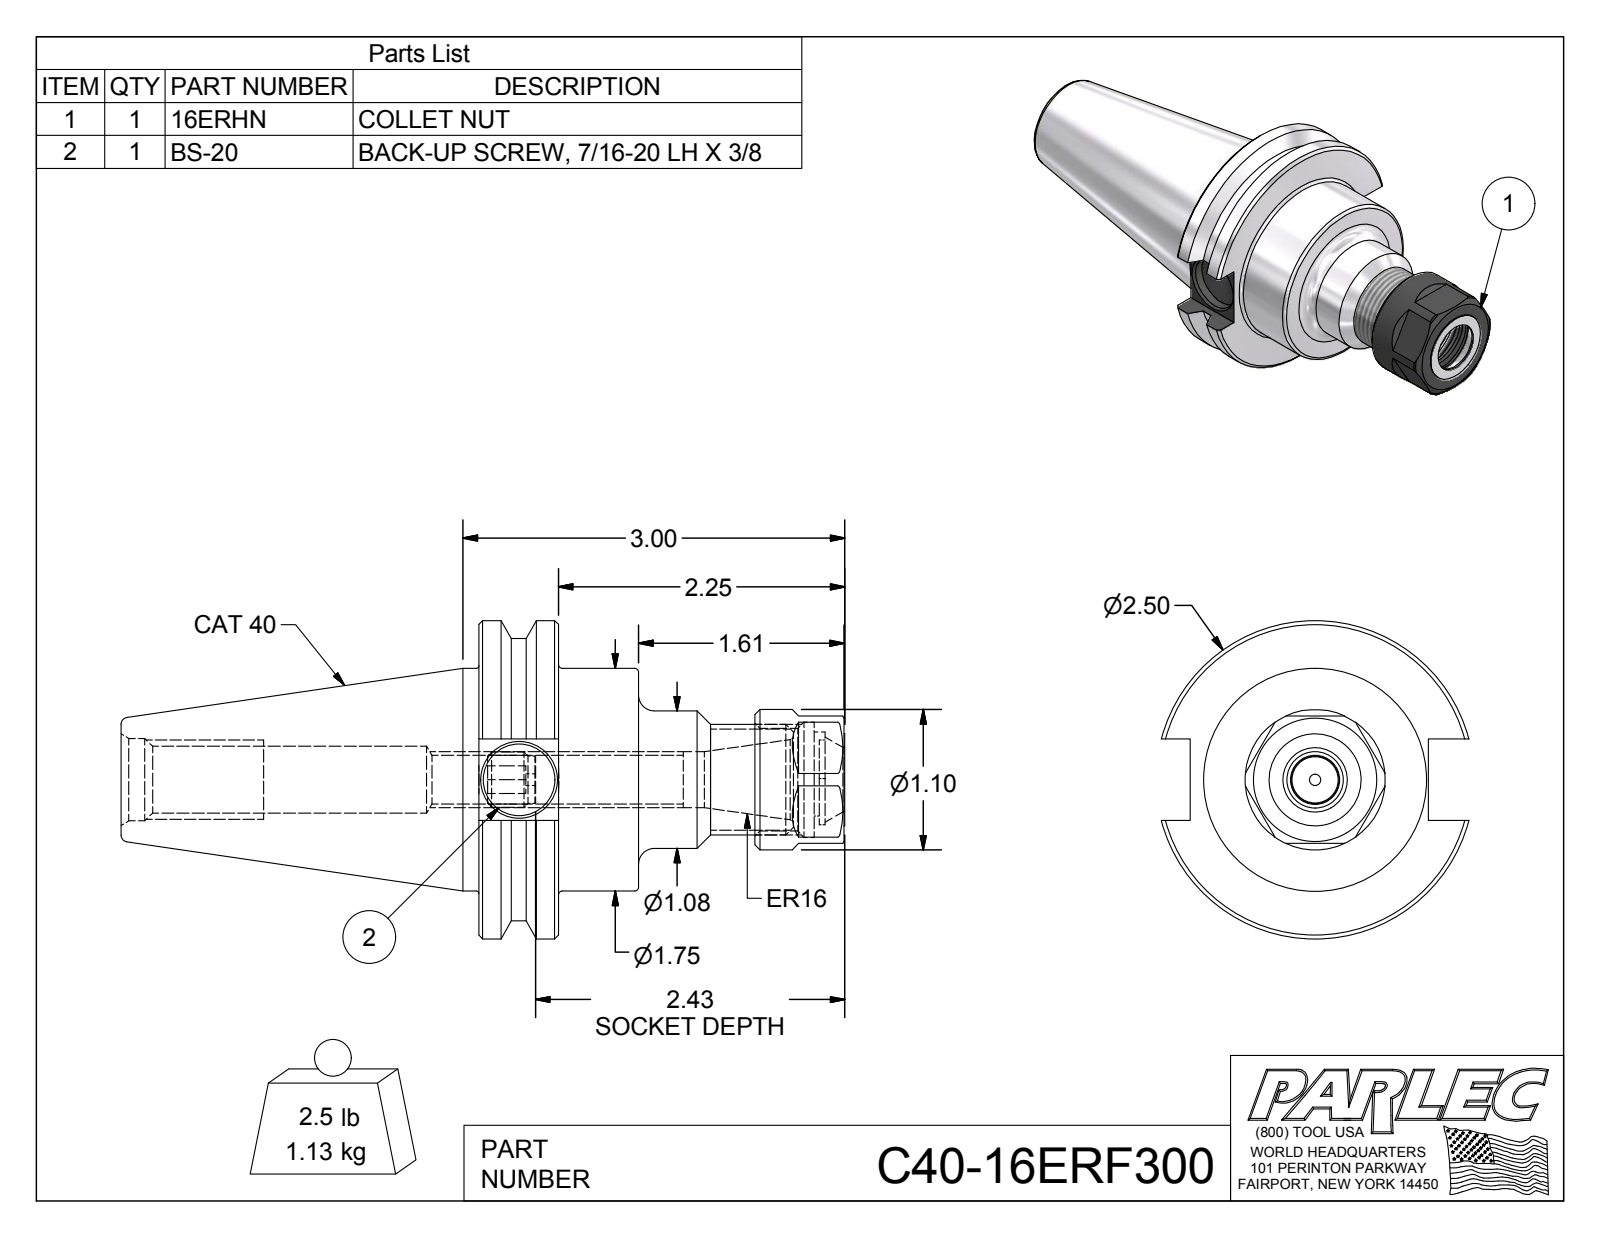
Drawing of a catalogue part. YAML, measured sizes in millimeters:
part_name: "C40-16ER3-1; 16ERHN; BS-20; C40-16ERF300"
step_written_by: "Autodesk Inventor 2016 (AUTOMOTIVE_DESIGN)"
units: millimeters
bodies: {solids: 3, faces: 102, planar: 39, cylindrical: 26, other: 37}
overall_size: [144.46, 63.5, 61.38]
volume: 142206
surface_area: 29874
round_holes:
  - {diameter: 2.29, count: 1}
  - {diameter: 8, count: 1}
  - {diameter: 9.73, count: 1}
  - {diameter: 10.13, count: 1}
  - {diameter: 11.18, count: 1}
  - {diameter: 12.4, count: 1}
  - {diameter: 13.39, count: 1}
  - {diameter: 16.46, count: 1}
  - {diameter: 17.02, count: 1}
  - {diameter: 20.5, count: 1}
  - {diameter: 23, count: 1}
round_bosses_or_shafts:
  - {diameter: 63.5, count: 1}
  - {diameter: 56.36, count: 1}
  - {diameter: 44.45, count: 1}
  - {diameter: 28, count: 1}
  - {diameter: 27.43, count: 1}
  - {diameter: 22, count: 1}
  - {diameter: 10.97, count: 1}
  - {diameter: 9.46, count: 1}
partial_cylinders:
  - {radius: 7.24, count: 1}
  - {radius: 9, count: 1}
face_to_face_distances: [15.88, 31.88, 16, 73.03, 57.15, 41.15, 25.14, 4.44, 20.7, 67.33]
hole_center_spacings: [1.52]
